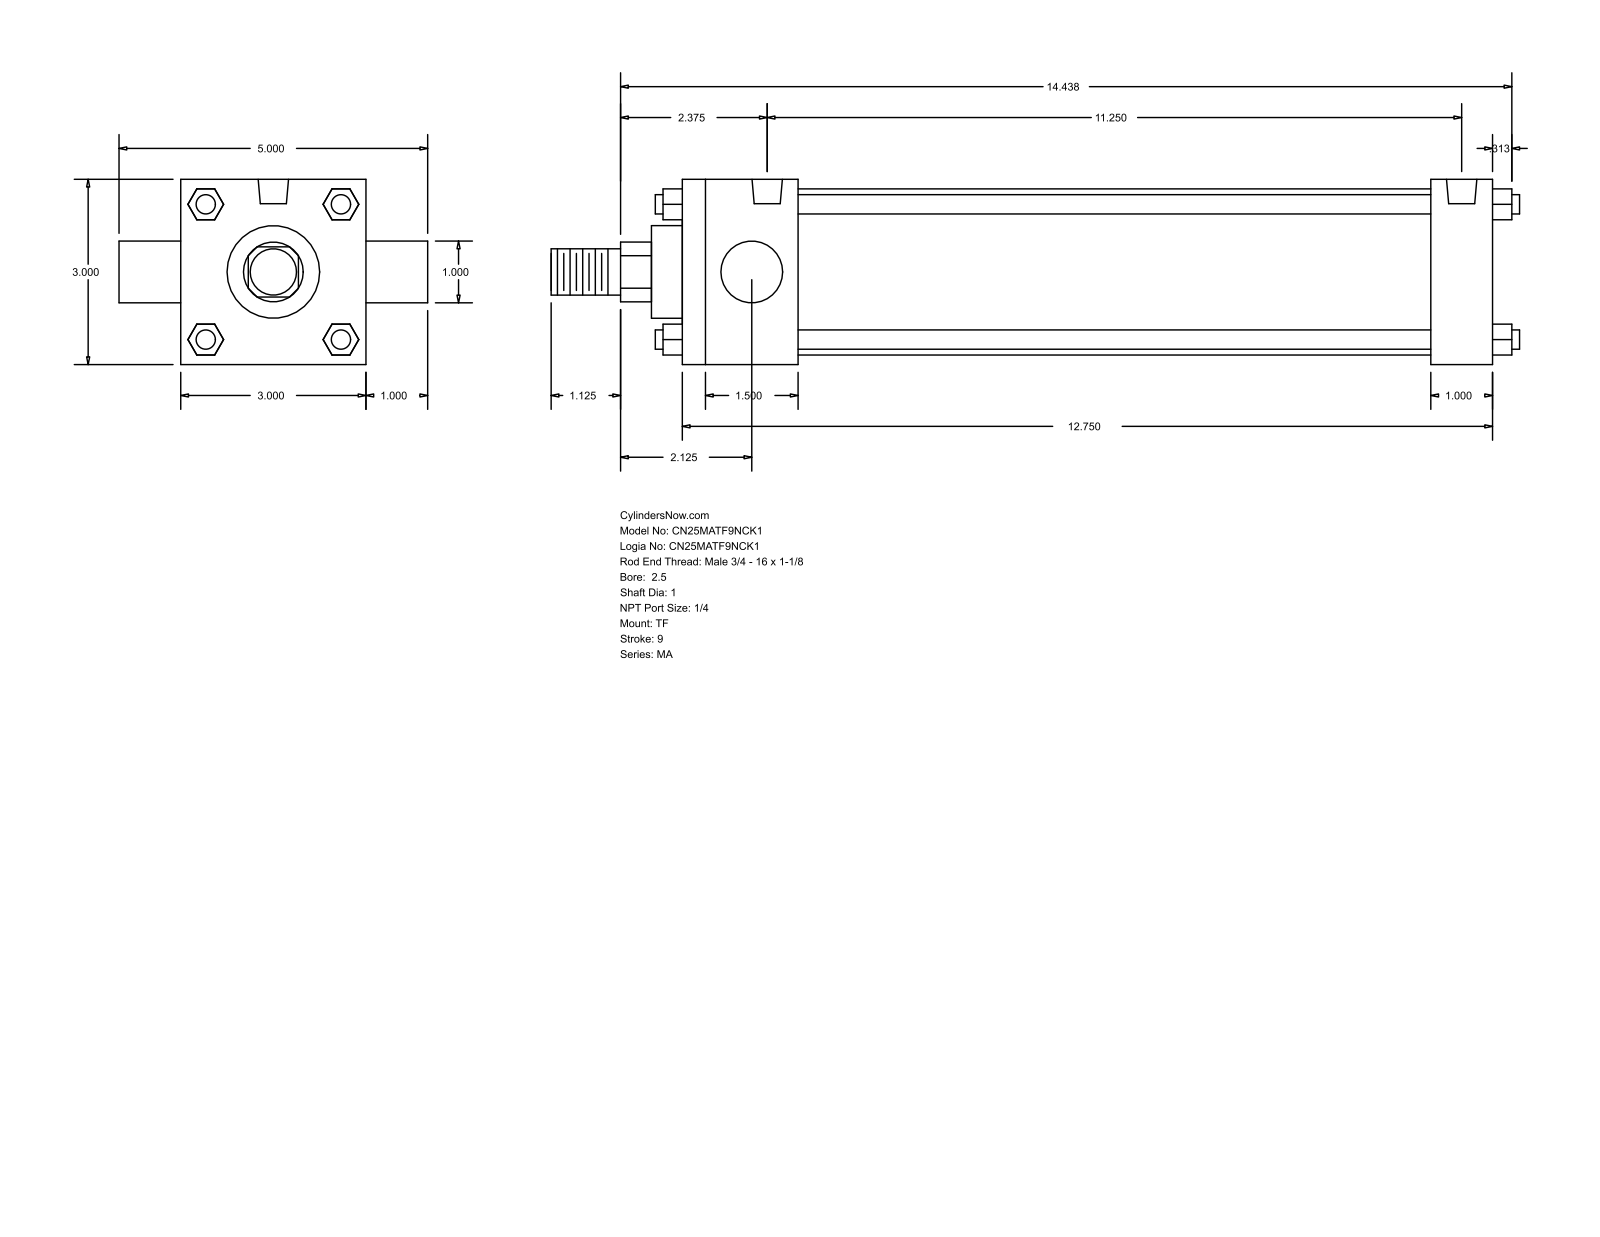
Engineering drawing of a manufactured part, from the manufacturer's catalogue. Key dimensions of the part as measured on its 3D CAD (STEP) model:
Part name (STEP PRODUCT): MA_TF__0250_1
STEP written by: GSSL Pune (CONFIG_CONTROL_DESIGN)
Units: millimetres
Bodies: 0 solids, 120 faces (92 planar, 28 cylindrical, 0 other)
Overall size (bounding box): 398.46 × 127 × 76.2
Round holes (diameter × count): ⌀7.94 ×3, ⌀12.49 ×2
Round bosses / shafts (diameter × count): ⌀7.94 ×4, ⌀25.4 ×2, ⌀68.33 ×1, ⌀38.1 ×1, ⌀19.05 ×1
Partial cylindrical surfaces — rounded edges, fillets, slot ends (radius × count): R12.29 ×1
Main face-to-face distances: 76.2, 333.37, 12.7, 47.63, 307.98, 260.35, 285.74, 25.39, 101.6, 25.4
Hole centre spacings: 285.74
